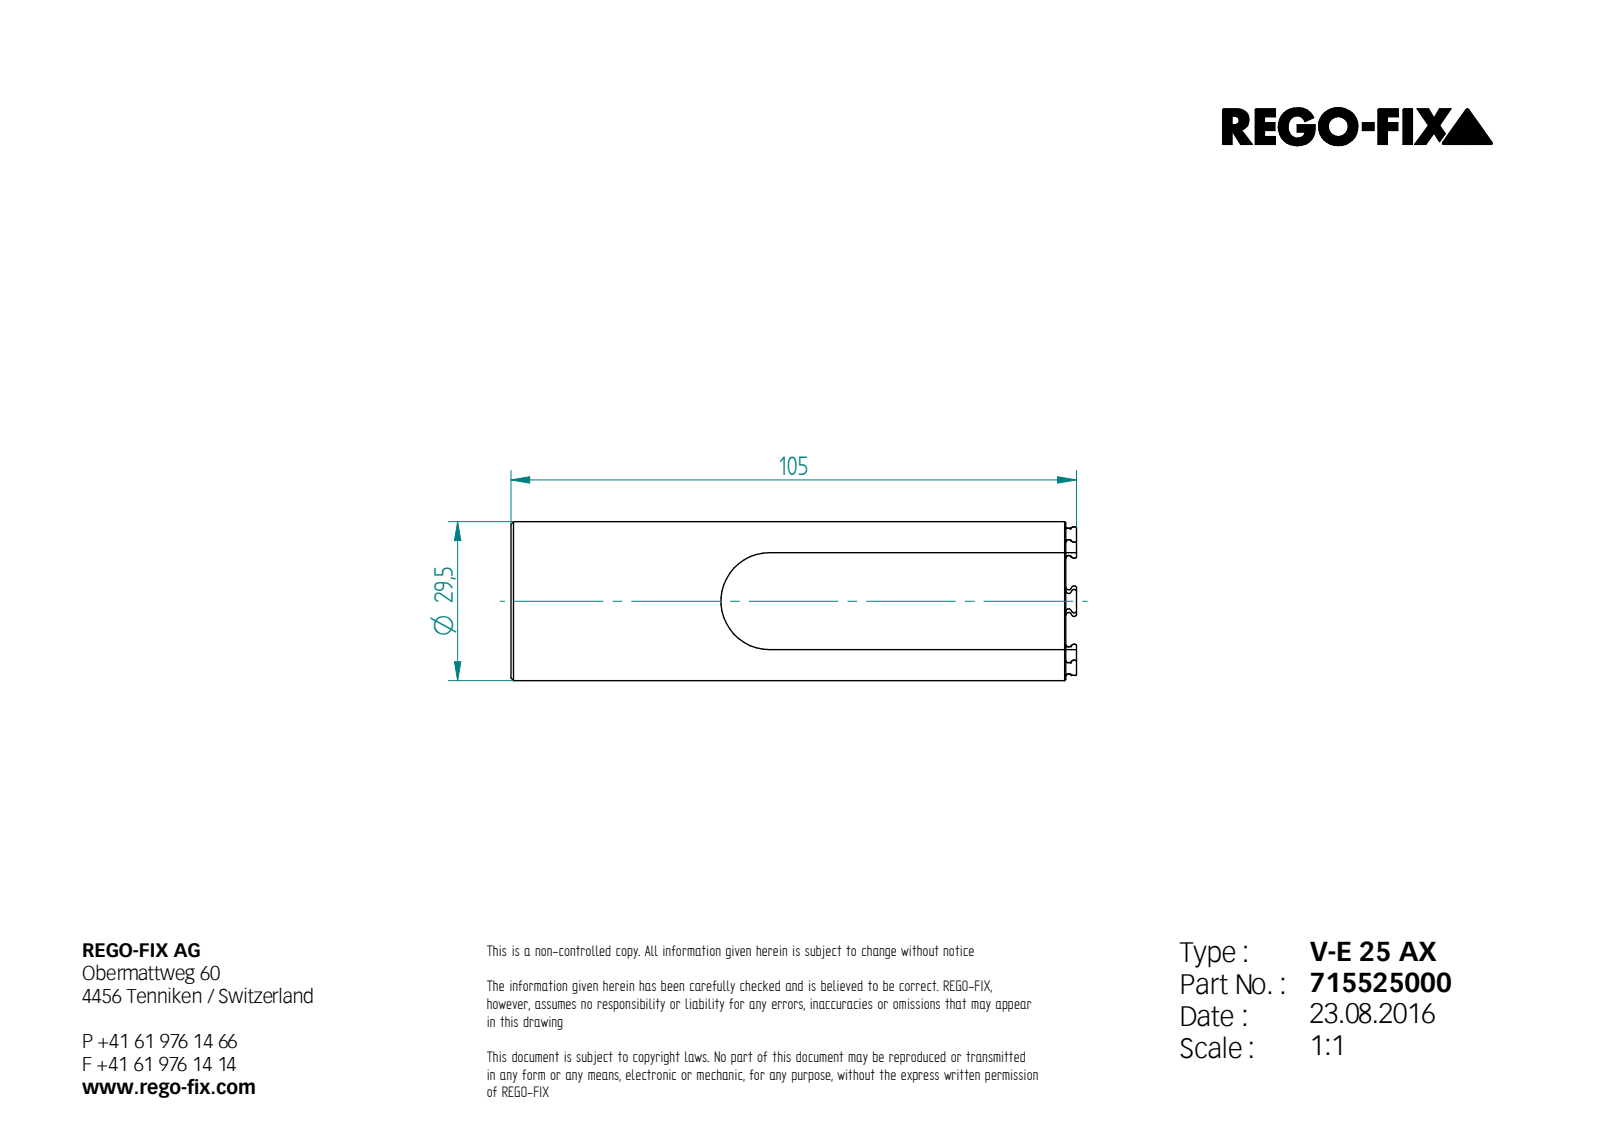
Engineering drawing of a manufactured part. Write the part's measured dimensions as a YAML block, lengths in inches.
step_written_by: "Unknown (AUTOMOTIVE_DESIGN)"
units: inches
bodies: {solids: 1, faces: 76, planar: 26, cylindrical: 21, other: 29}
overall_size: [4.134, 1.161, 1.161]
volume: 2.047
surface_area: 23.71
round_holes:
  - {diameter: 0.827, count: 1}
round_bosses_or_shafts:
  - {diameter: 1.161, count: 1}
partial_cylinders:
  - {radius: 0.266, count: 1}
  - {radius: 0.354, count: 1}
  - {radius: 0.421, count: 1}
  - {radius: 0.573, count: 1}
face_to_face_distances: [0.709, 0.1, 0.608, 0.508, 4.055, 4.134, 0.079, 0.685]
